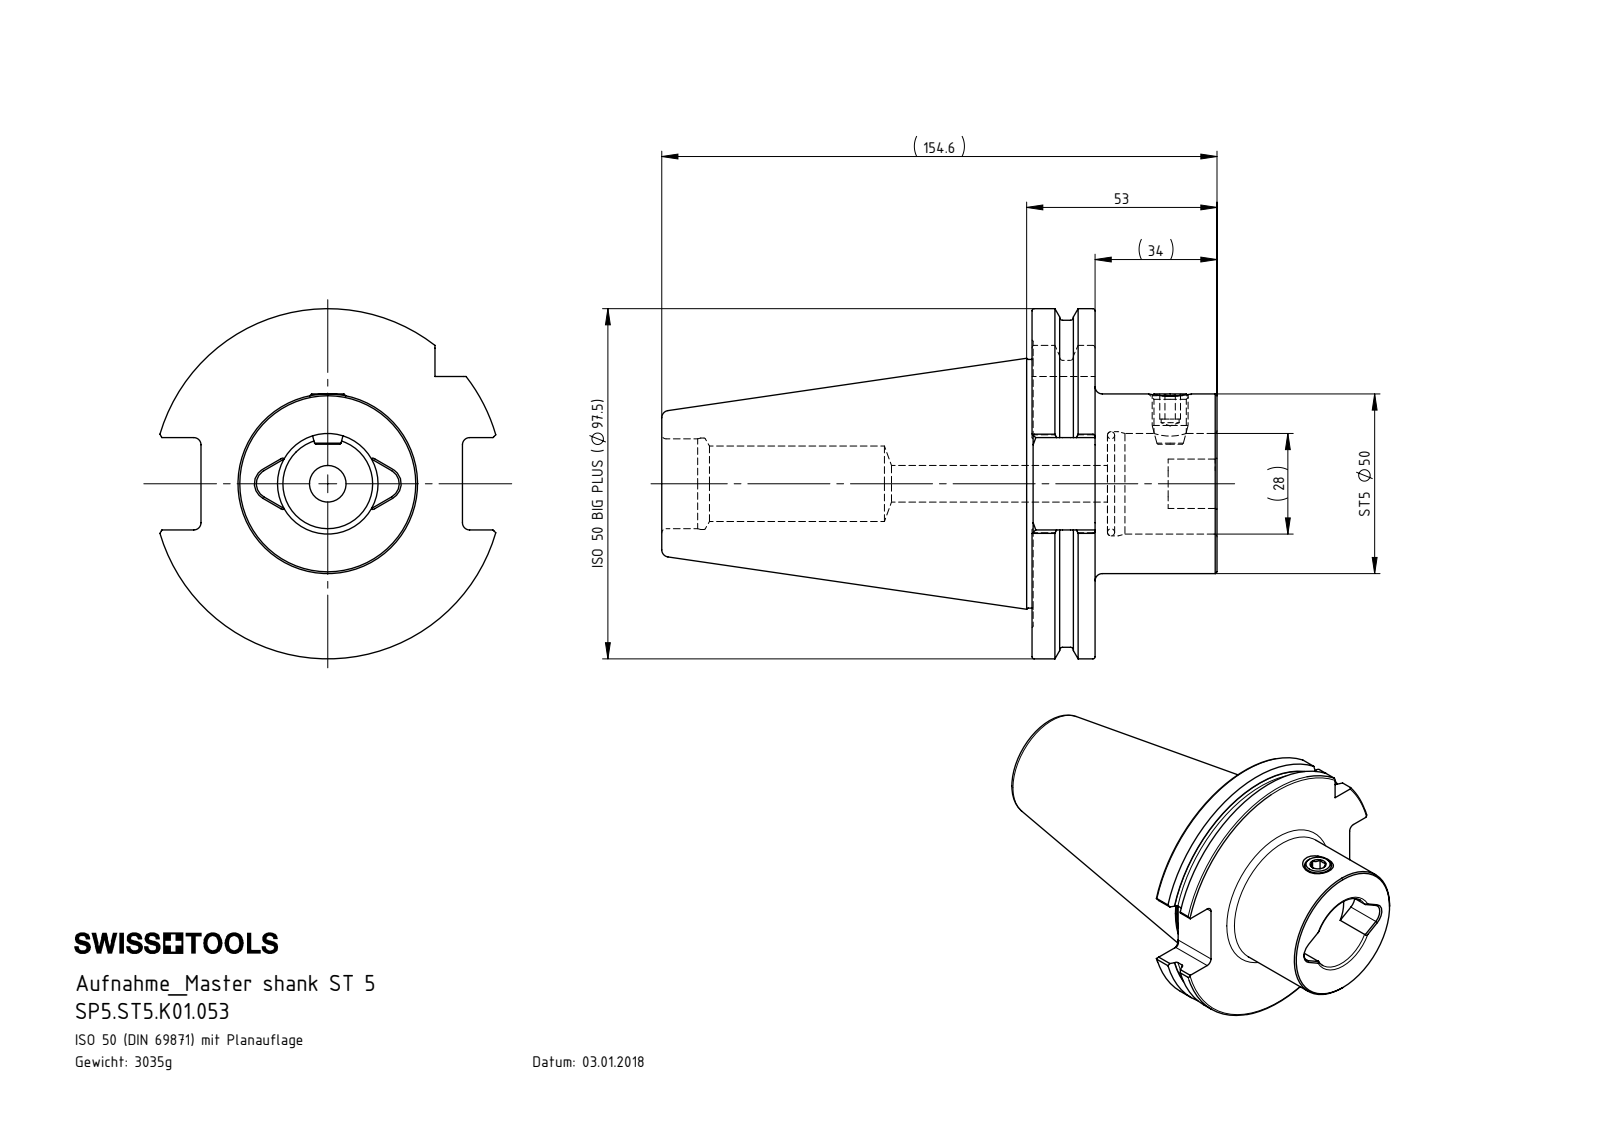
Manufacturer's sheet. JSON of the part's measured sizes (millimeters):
{"part_name": "ST5-ER1.001.012_A; SP5-ST5.K01.053_A; SP5.ST5.K01.053; DIN 3771 - 25x2", "step_written_by": "SolidWorks 2017 (AUTOMOTIVE_DESIGN)", "units": "millimeters", "bodies": {"solids": 3, "faces": 134, "planar": 55, "cylindrical": 30, "other": 49}, "overall_size": [154.6, 97.45, 93.51], "volume_mm3": 386864, "surface_area_mm2": 51217, "round_holes": [[5, 1], [9, 1], [10.2, 1], [21, 1], [25, 1], [25.45, 1], [28, 1], [29, 1]], "round_bosses_or_shafts": [[91, 1], [69.2, 1], [50, 1], [10, 1]], "partial_cylinders_radius": [[1.9, 4], [2, 4], [4.2, 2], [48.73, 1]], "face_to_face_distances": [17.55, 51.5, 33.95, 17.25, 51.2, 21, 20.7, 3.45, 30.5, 103.1]}
